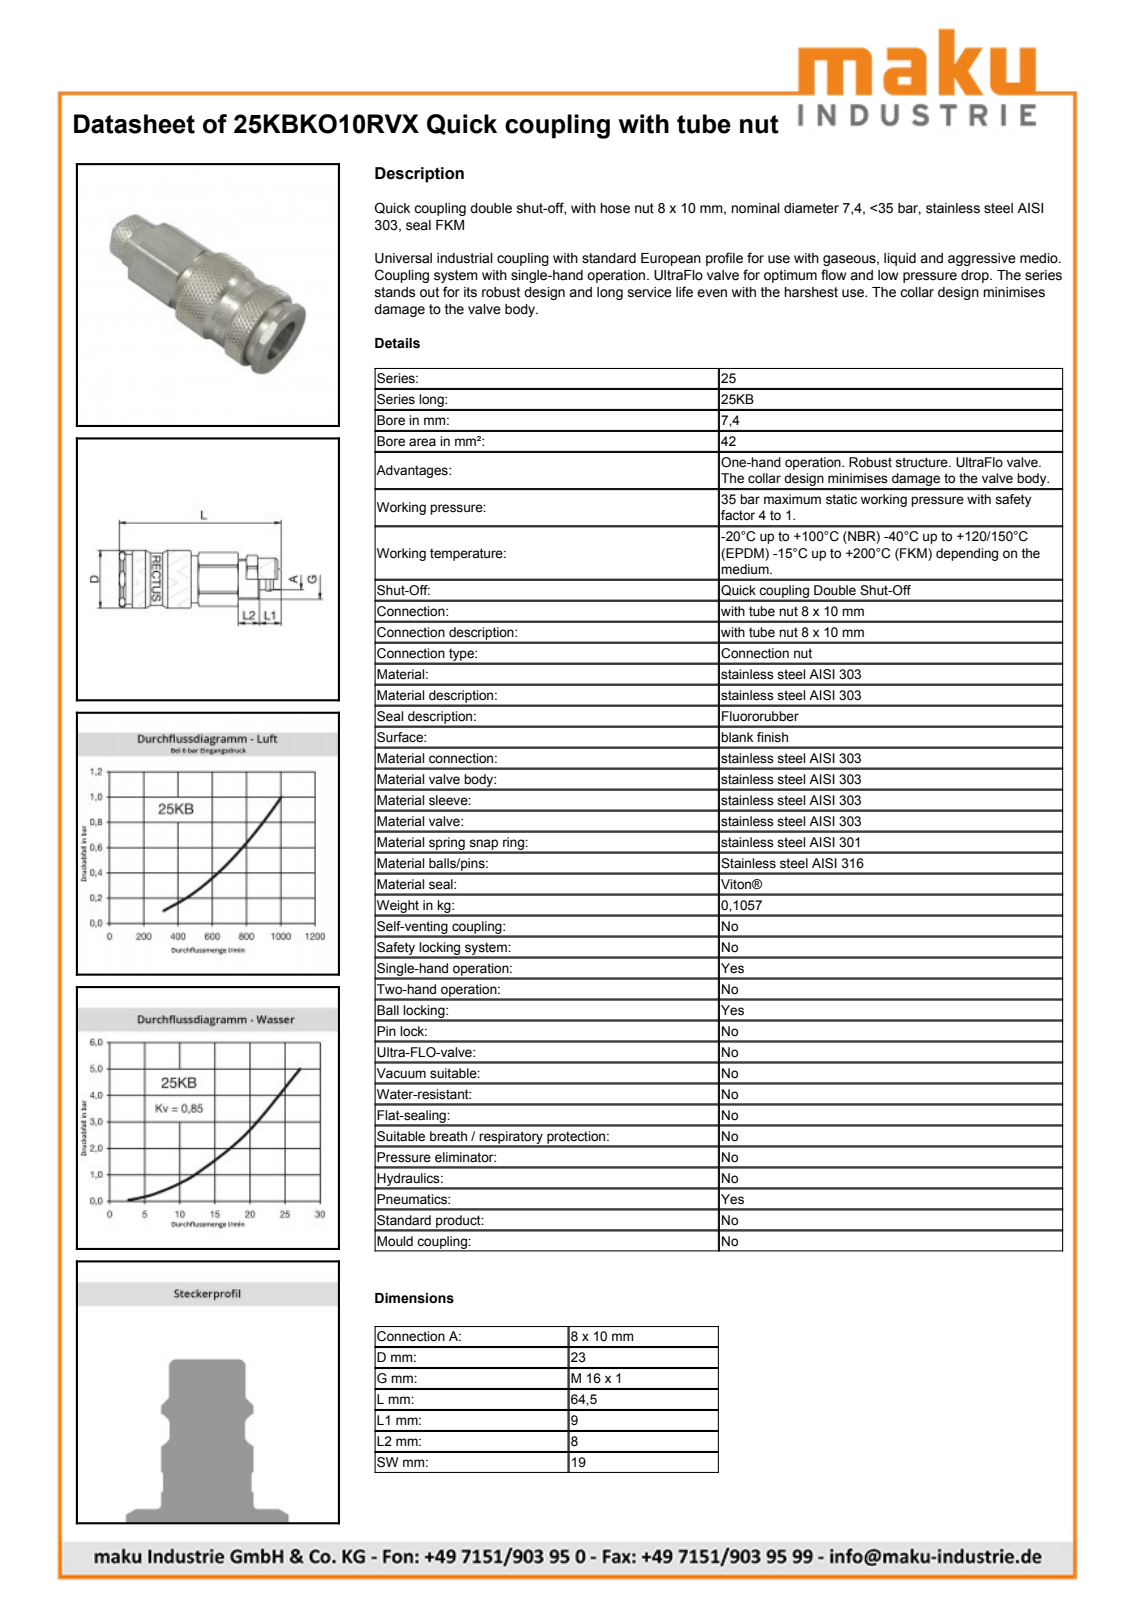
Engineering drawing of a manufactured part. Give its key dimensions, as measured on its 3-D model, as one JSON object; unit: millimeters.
{"part_name": "D105951", "step_written_by": "Autodesk Inventor 2011 (AUTOMOTIVE_DESIGN)", "units": "millimeters", "bodies": {"solids": 2, "faces": 654, "planar": 223, "cylindrical": 97, "other": 334}, "overall_size": [64.5, 23.15, 23.15], "volume_mm3": 18347, "surface_area_mm2": 9047, "round_holes": [[10.2, 1], [15.1, 1], [15.6, 1], [17.25, 1], [19.35, 1], [20.05, 1]], "round_bosses_or_shafts": [[23.15, 1], [21, 1], [20, 1], [18.95, 1], [17, 1], [16, 1], [15.3, 1], [15, 1]], "partial_cylinders_radius": [[9.4, 1], [10.4, 1], [10.7, 1], [11, 1]], "face_to_face_distances": [19, 17, 55.9, 59.4, 3.5, 61.4, 5.5, 2, 47.5, 8.4]}
